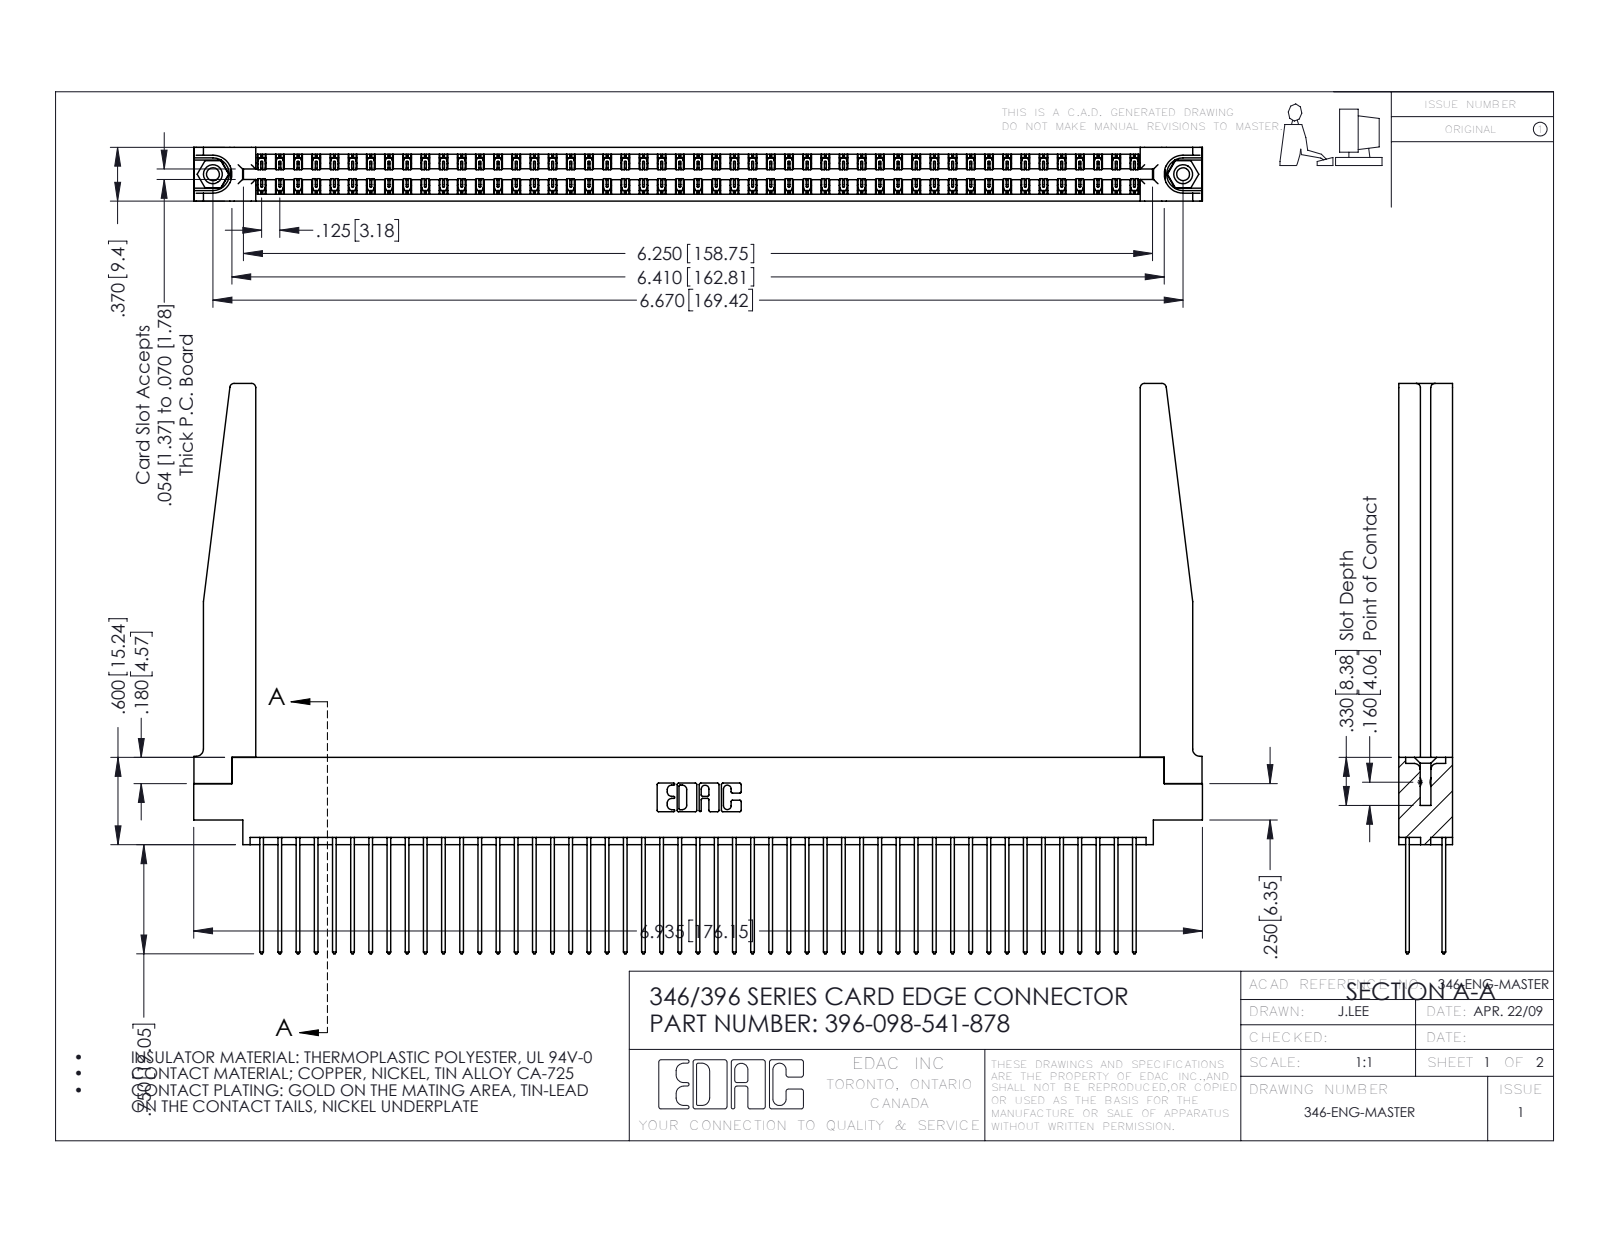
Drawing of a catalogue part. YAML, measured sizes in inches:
part_name: "345-250-001_345-250-001-102; 346 Part_0.170 Offset - 0.156 Dia-TH; 396-098-541-878; 346-220-078_345-220-078 (+1 more)"
step_written_by: "SolidWorks 2016 (CONFIG_CONTROL_DESIGN)"
units: inches
bodies: {solids: 103, faces: 5456, planar: 3652, cylindrical: 1752, other: 52}
overall_size: [6.935, 3.92, 0.37]
volume: 1.498
surface_area: 52.34
round_holes:
  - {diameter: 0.089, count: 2}
  - {diameter: 0.125, count: 2}
  - {diameter: 0.156, count: 2}
  - {diameter: 0.064, count: 1}
round_bosses_or_shafts:
  - {diameter: 0.155, count: 2}
partial_cylinders:
  - {radius: 0.006, count: 147}
  - {radius: 0.01, count: 98}
  - {radius: 0.01, count: 22}
  - {radius: 0.03, count: 8}
  - {radius: 0.007, count: 6}
  - {radius: 0.031, count: 6}
  - {radius: 0.026, count: 3}
  - {radius: 0.014, count: 2}
face_to_face_distances: [0.048, 0.322, 0.37, 0.072, 0.25, 0.298, 0.025, 0.275, 0.15, 0.148]
hole_center_spacings: [0.246, 6.461, 6.67]
